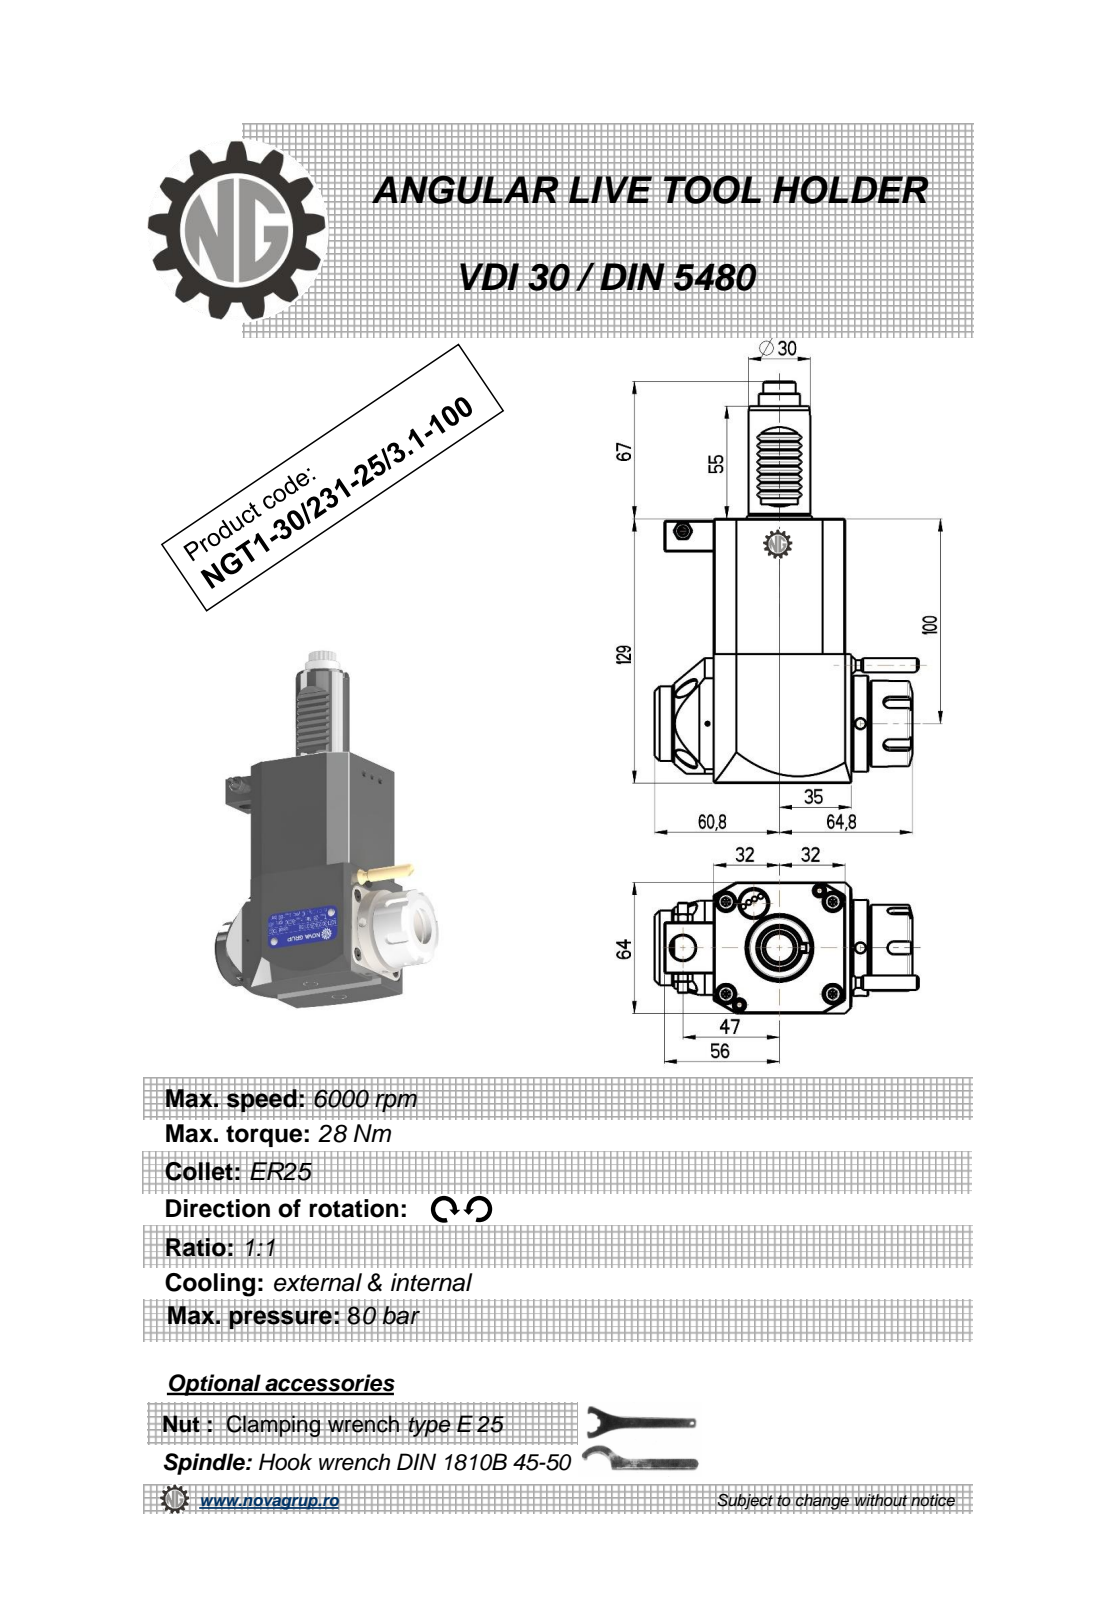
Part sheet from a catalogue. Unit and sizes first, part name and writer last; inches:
Units: inches
Overall size (bounding box): 7.717 × 5.064 × 2.52
Round holes (diameter × count): ⌀0.197 ×2, ⌀0.098 ×1, ⌀0.118 ×1, ⌀0.165 ×1, ⌀0.374 ×1, ⌀0.472 ×1, ⌀0.799 ×1
Round bosses / shafts (diameter × count): ⌀0.353 ×2, ⌀0.197 ×2, ⌀1.85 ×1, ⌀1.654 ×1, ⌀1.437 ×1, ⌀1.378 ×1, ⌀1.181 ×1, ⌀0.787 ×1
Partial cylindrical surfaces — rounded edges, fillets, slot ends (radius × count): R0.078 ×36, R0.01 ×12, R0.012 ×8, R0.118 ×5, R6.299 ×2, R0.279 ×1, R0.312 ×1, R0.512 ×1
Main face-to-face distances: 2.52, 5.079, 3.009, 0.02, 2.646, 0.126, 2.638, 0.295, 0.118, 0.315
Hole centre spacings: 1.307, 2.569, 3.404, 3.602, 5.028
Volume: 40.19 in³ · Surface area: 93.55 in²
Bodies: 1 solid, 515 faces (194 planar, 155 cylindrical, 166 other)
Part name (STEP PRODUCT): NGT1_30_231_25_3_1_100
STEP written by: PRO/ENGINEER BY PARAMETRIC TECHNOLOGY CORPORATION, 2010280 (CONFIG_CONTROL_DESIGN)
